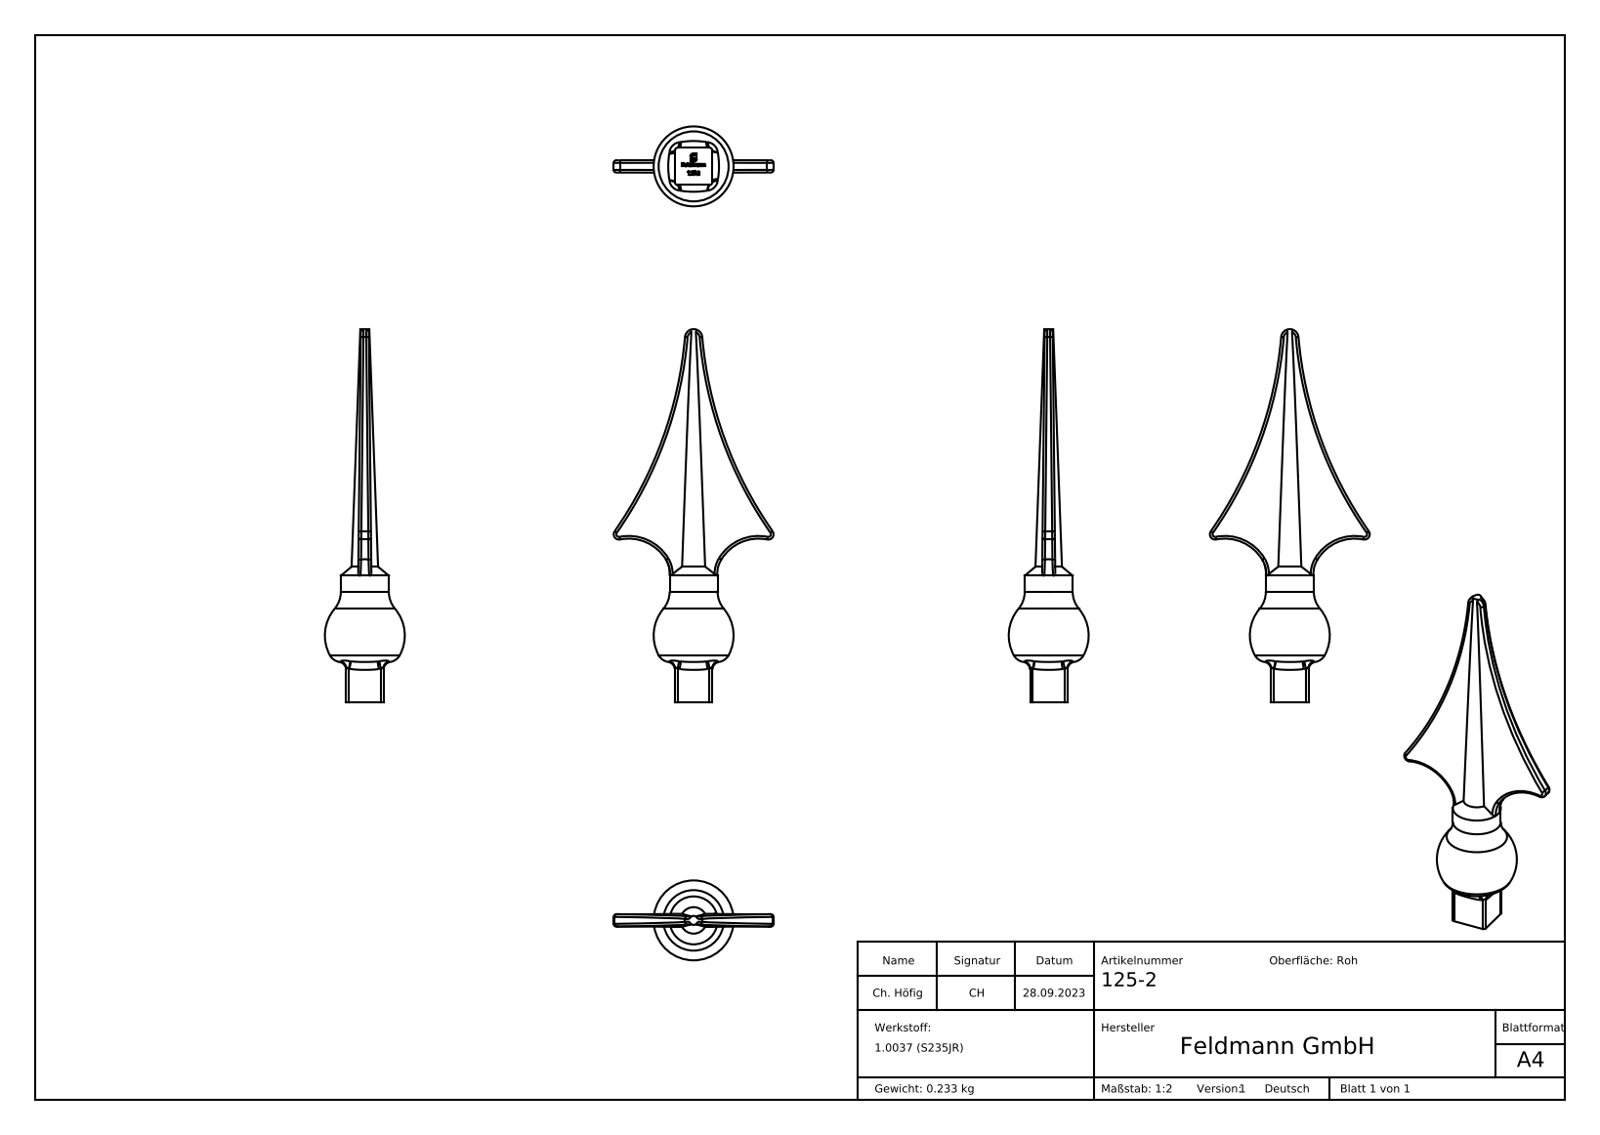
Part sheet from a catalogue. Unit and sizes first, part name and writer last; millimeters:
Units: millimetres
Overall size (bounding box): 140 × 60 × 26.27
Round bosses / shafts (diameter × count): ⌀18 ×1
Partial cylindrical surfaces — rounded edges, fillets, slot ends (radius × count): R1 ×4, R2 ×2, R16.36 ×2, R150 ×2, R3.26 ×1
Main face-to-face distances: 14, 2.4, 2.52, 1.14, 3.27, 3.8, 0.63, 4.85, 0.34, 2.84
Volume: 29 869 mm³ · Surface area: 9 562 mm²
Bodies: 1 solid, 275 faces (130 planar, 12 cylindrical, 133 other)
Part name (STEP PRODUCT): 125-2
STEP written by: SolidWorks 2018 (CONFIG_CONTROL_DESIGN)
